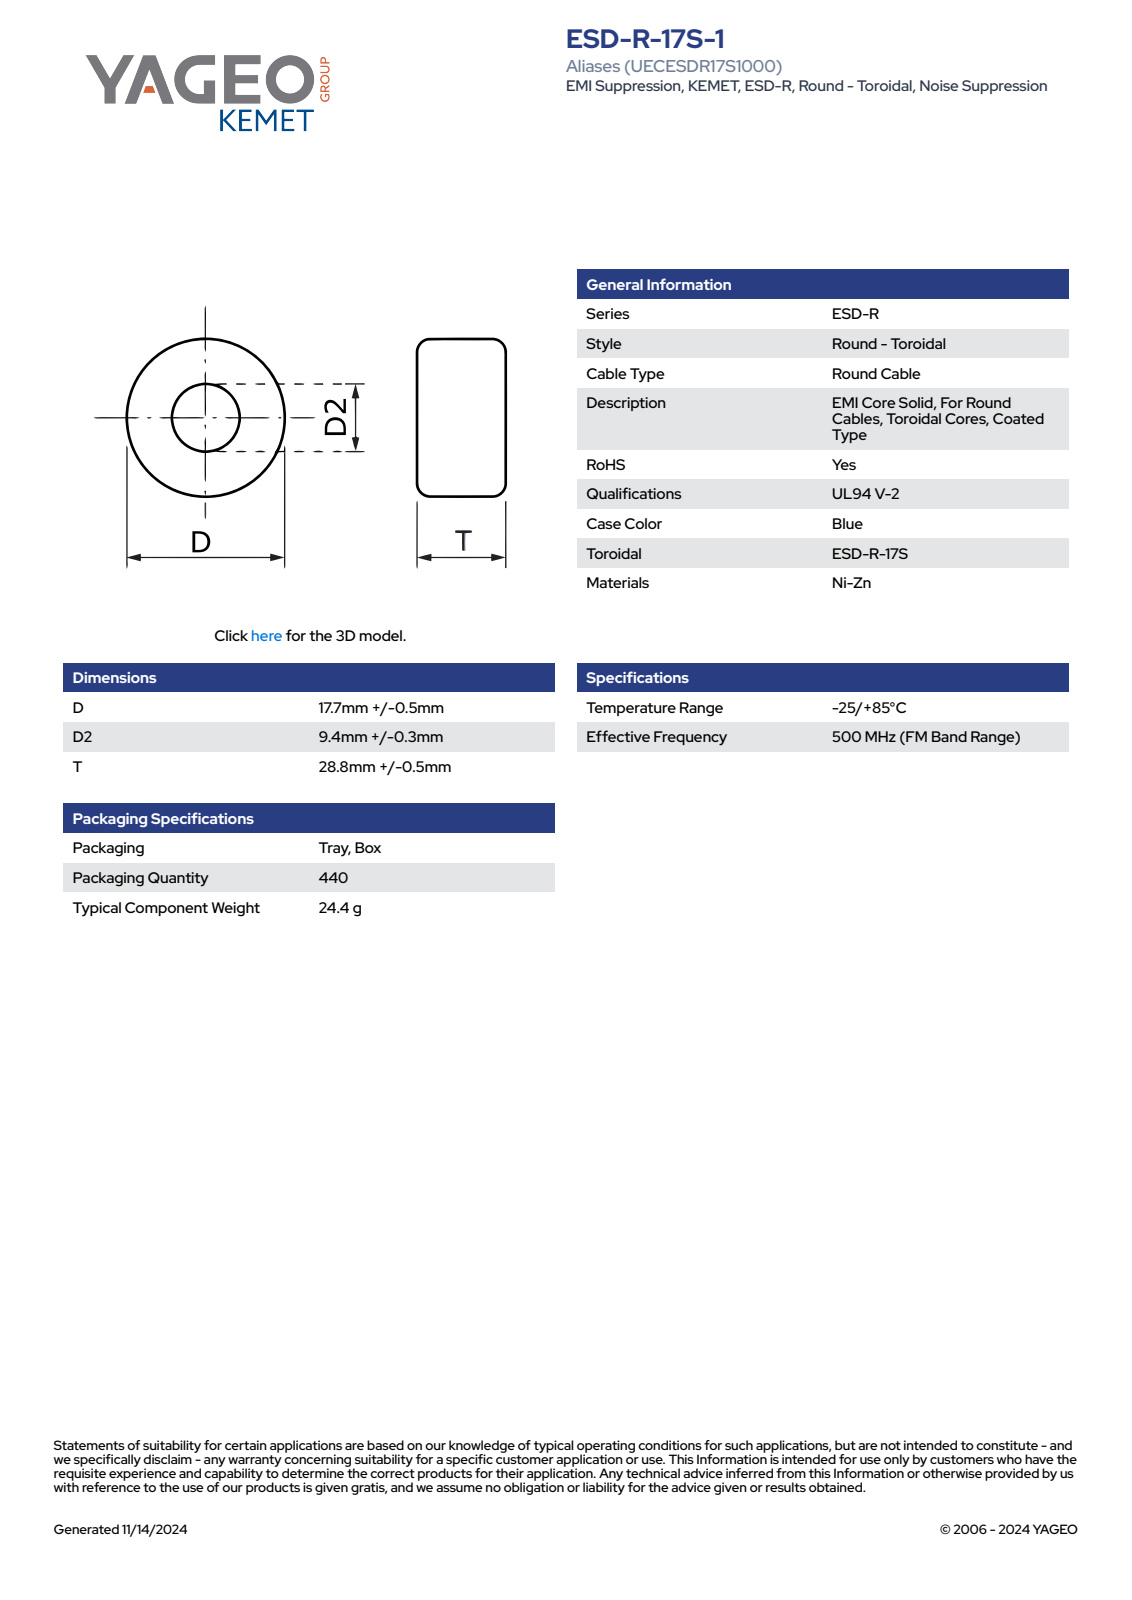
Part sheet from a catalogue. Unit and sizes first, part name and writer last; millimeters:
Units: millimetres
Overall size (bounding box): 29.3 × 18.21 × 18.2
Round holes (diameter × count): ⌀9.4 ×1
Round bosses / shafts (diameter × count): ⌀18.2 ×1
Partial cylindrical surfaces — rounded edges, fillets, slot ends (radius × count): R9.11 ×1
Main face-to-face distances: 29.3, 13.8, 15.5, 1.7, 0.32, 14.12, 15.18, 1.38, 1.06, 14.86
Volume: 5 581 mm³ · Surface area: 2 897 mm²
Bodies: 1 solid, 66 faces (24 planar, 7 cylindrical, 35 other)
Part name (STEP PRODUCT): EC_KBC_D18.2D29.4T29.3
STEP written by: SolidWorks 2021 (AUTOMOTIVE_DESIGN)
